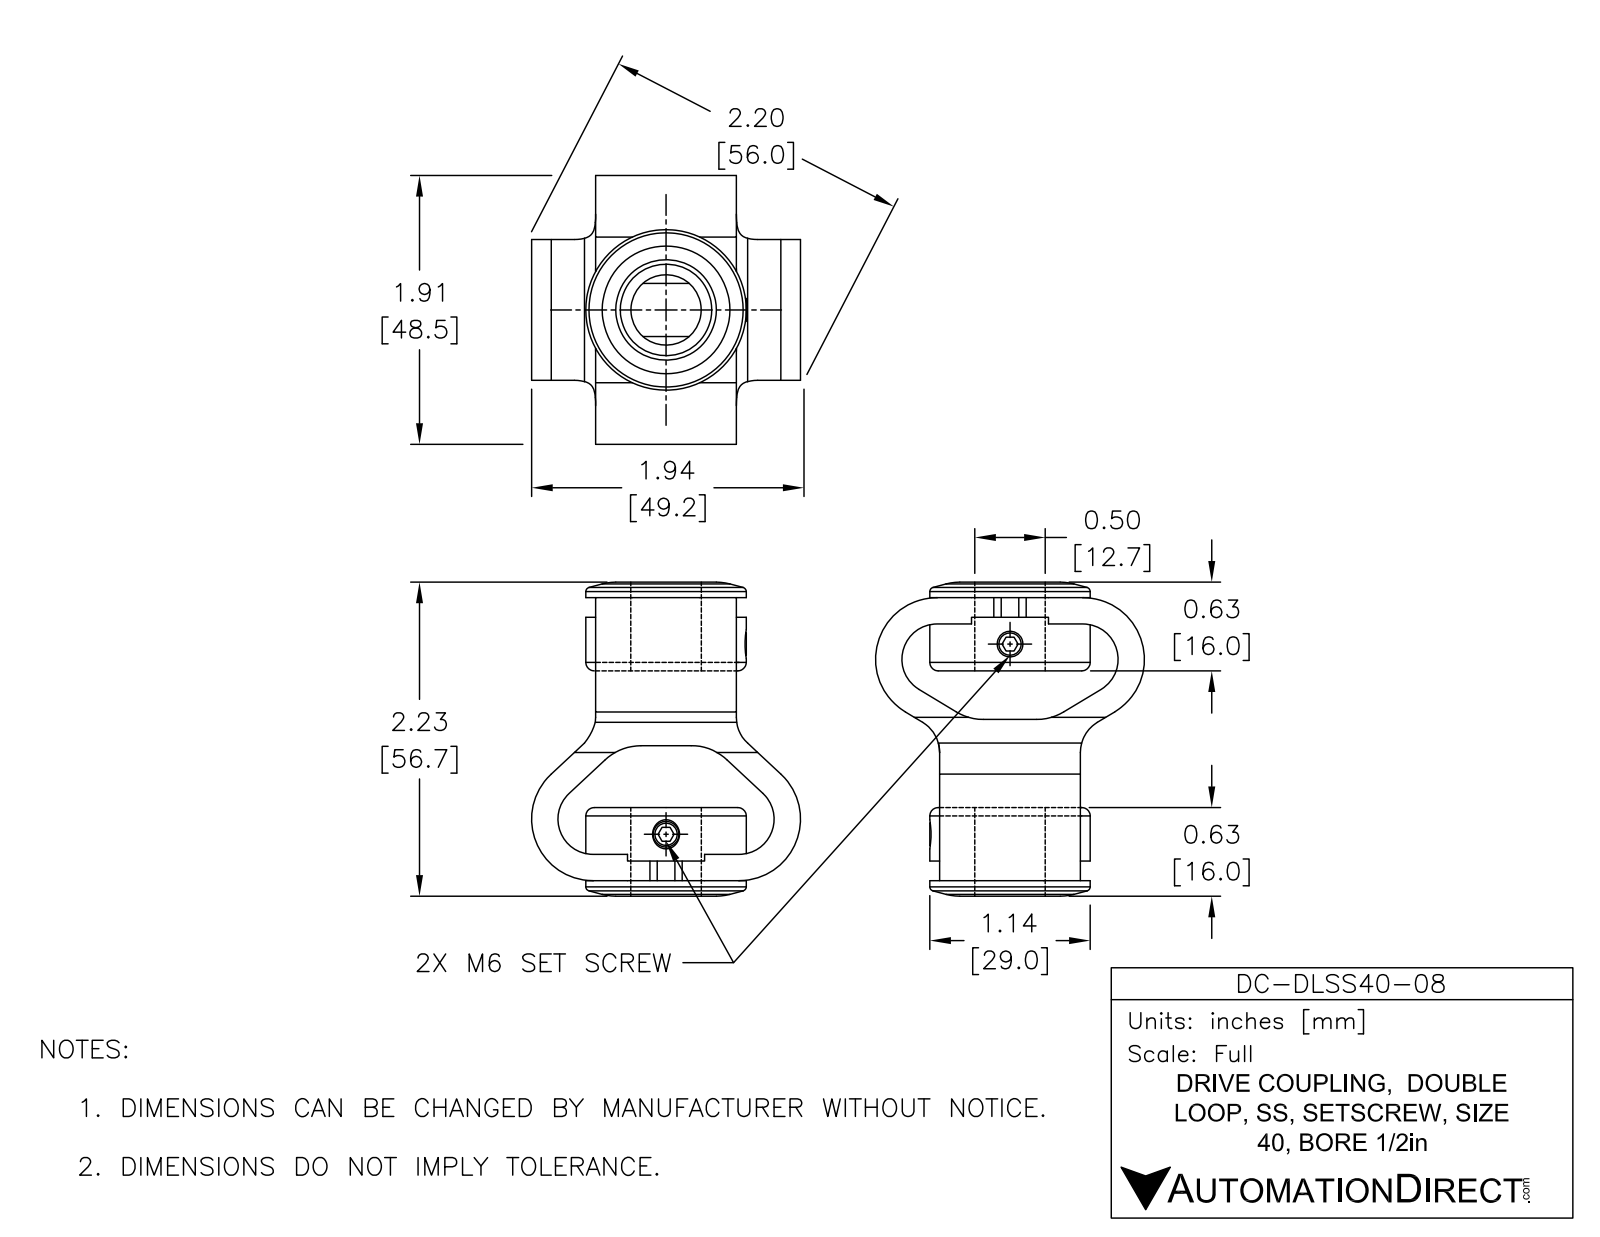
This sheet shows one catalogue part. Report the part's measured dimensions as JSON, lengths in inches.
{"part_name": "DC-DLSS40-08", "step_written_by": "SolidWorks 2015 (AUTOMOTIVE_DESIGN)", "units": "inches", "bodies": {"solids": 1, "faces": 187, "planar": 90, "cylindrical": 49, "other": 48}, "overall_size": [2.231, 1.91, 1.91], "volume_in3": 2.105, "surface_area_in2": 23.38, "round_holes": [[0.163, 2], [0.5, 1]], "round_bosses_or_shafts": [[1.14, 1]], "partial_cylinders_radius": [[0.25, 8], [0.25, 4], [0.375, 4], [0.437, 3], [0.41, 1], [0.437, 1]], "face_to_face_distances": [1, 0.187, 0.971, 0.626, 0.345, 0.11, 2.121, 0.439, 0.532, 0.865]}
